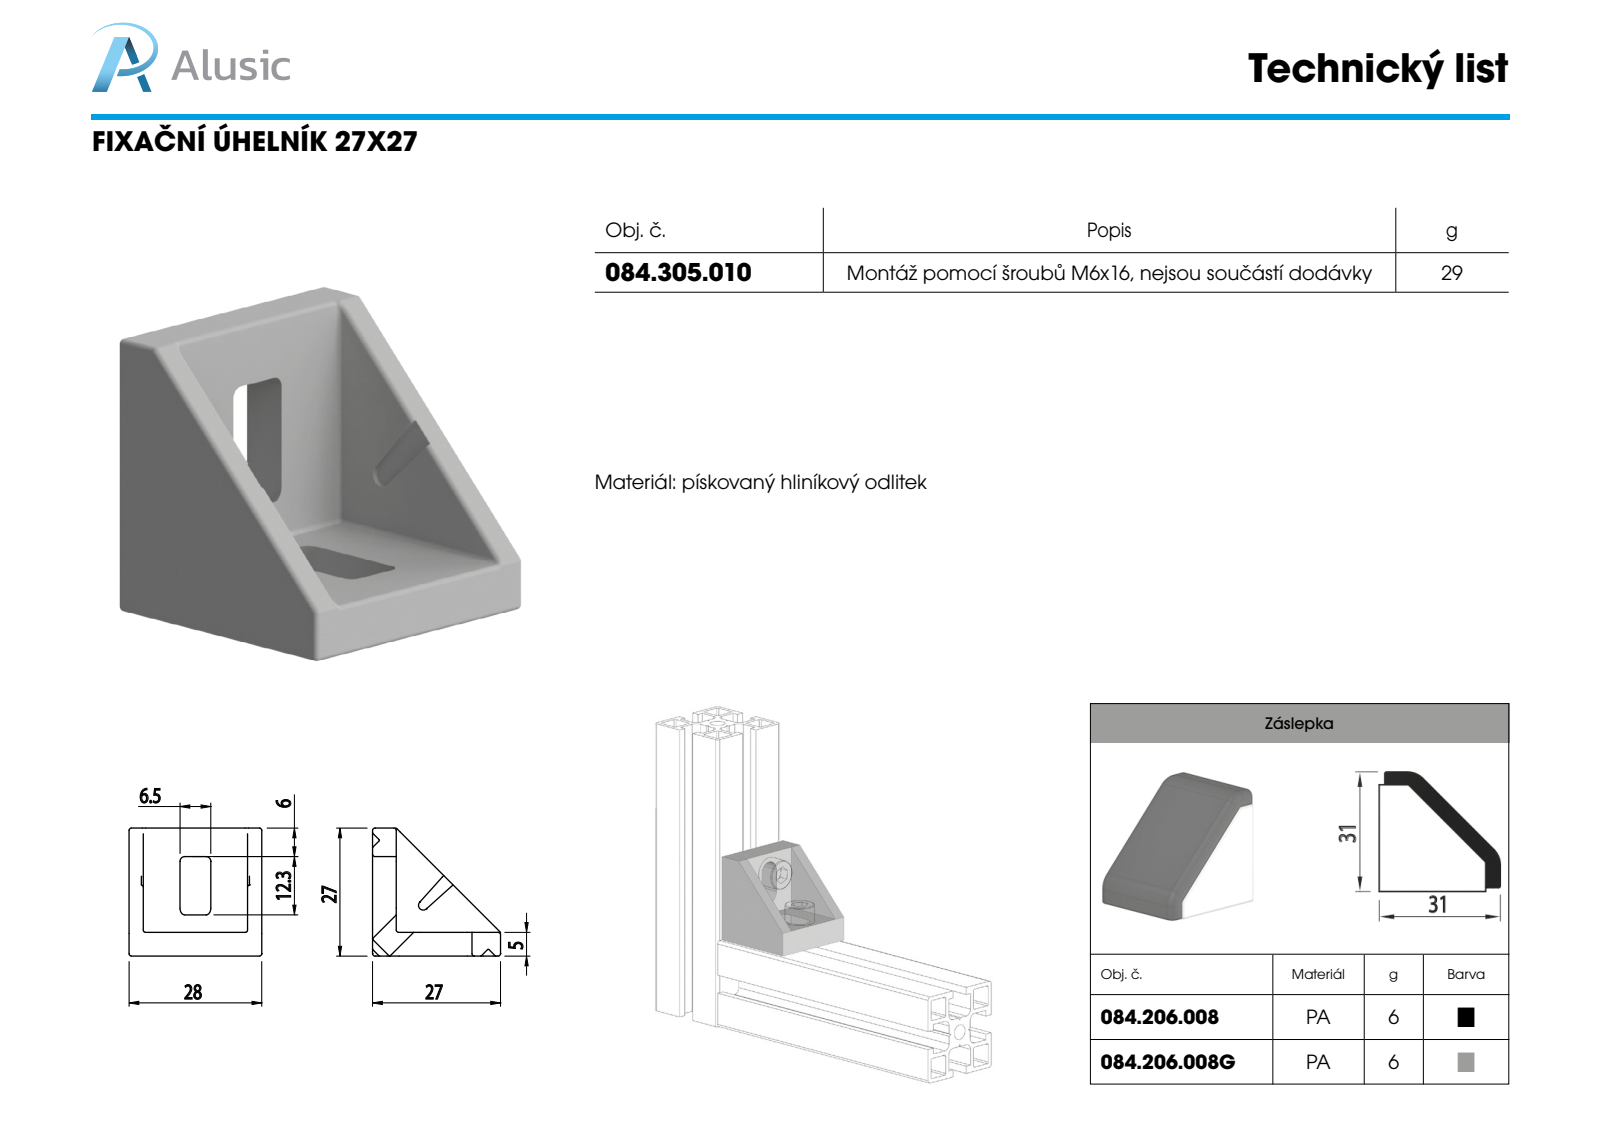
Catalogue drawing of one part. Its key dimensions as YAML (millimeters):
part_name: "084.305.010"
step_written_by: "SolidWorks 2016 (CONFIG_CONTROL_DESIGN)"
units: millimeters
bodies: {solids: 1, faces: 326, planar: 61, cylindrical: 149, other: 116}
overall_size: [28, 27, 27]
volume: 6572
surface_area: 4563
partial_cylinders:
  - {radius: 0.5, count: 44}
  - {radius: 0.2, count: 32}
  - {radius: 1, count: 21}
  - {radius: 0.4, count: 12}
  - {radius: 0.1, count: 10}
face_to_face_distances: [5, 28, 3, 22, 25, 7.75, 17.25, 1.7, 3.3, 27]
